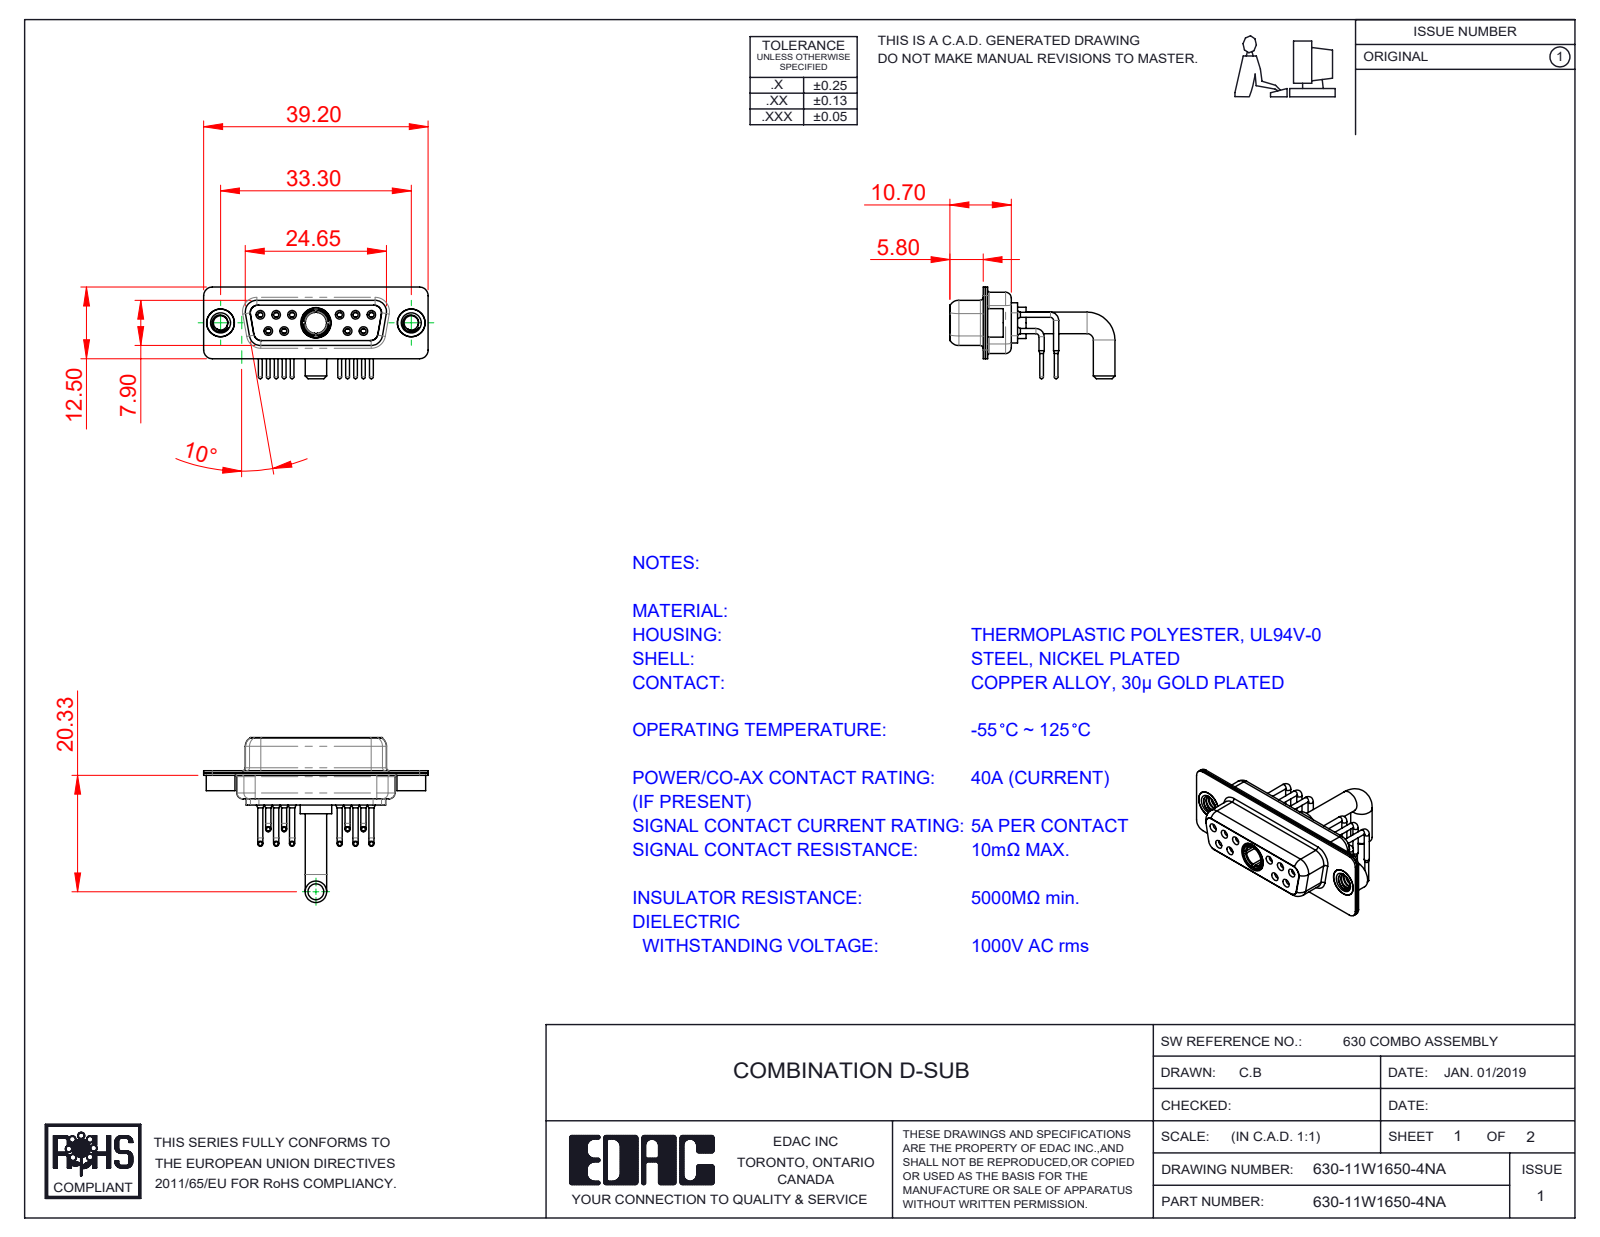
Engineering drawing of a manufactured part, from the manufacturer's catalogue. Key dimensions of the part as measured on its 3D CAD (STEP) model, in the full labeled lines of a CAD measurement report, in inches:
Part name (STEP PRODUCT): 630Combo Contact Row 1; 630Combo Contact Row 2; 630Combo Threaded Rivet_A; 630Combo Housing_11W1 (+4 more)
STEP written by: SolidWorks 2020 (CONFIG_CONTROL_DESIGN)
Units: inches
Bodies: 17 solids, 881 faces (246 planar, 390 cylindrical, 245 other)
Overall size (bounding box): 1.543 × 1.134 × 0.63
Volume: 0.17 in³ · Surface area: 9.925 in²
Round holes (diameter × count): ⌀0.035 ×10, ⌀0.043 ×10, ⌀0.059 ×10, ⌀0.079 ×10, ⌀0.067 ×6, ⌀0.063 ×4, ⌀0.191 ×3, ⌀0.098 ×2, ⌀0.157 ×2, ⌀0.159 ×2, ⌀0.146 ×1, ⌀0.209 ×1
Round bosses / shafts (diameter × count): ⌀0.035 ×10, ⌀0.026 ×10, ⌀0.063 ×6, ⌀0.197 ×2, ⌀0.195 ×2, ⌀0.189 ×2, ⌀0.148 ×2, ⌀0.217 ×1
Partial cylindrical surfaces — rounded edges, fillets, slot ends (radius × count): R0.059 ×16, R0.053 ×12, R0.079 ×12, R0.063 ×8, R0.01 ×4, R0.02 ×4, R0.024 ×4, R0.026 ×4
Main face-to-face distances: 0.016, 0.055, 0.018, 0.333, 0.071, 0.35, 0.031, 0.244, 0.278, 0.073
Hole centre spacings: 0.124, 0.109, 0.545, 0.436, 0.654, 0.198, 0.198, 0.218
